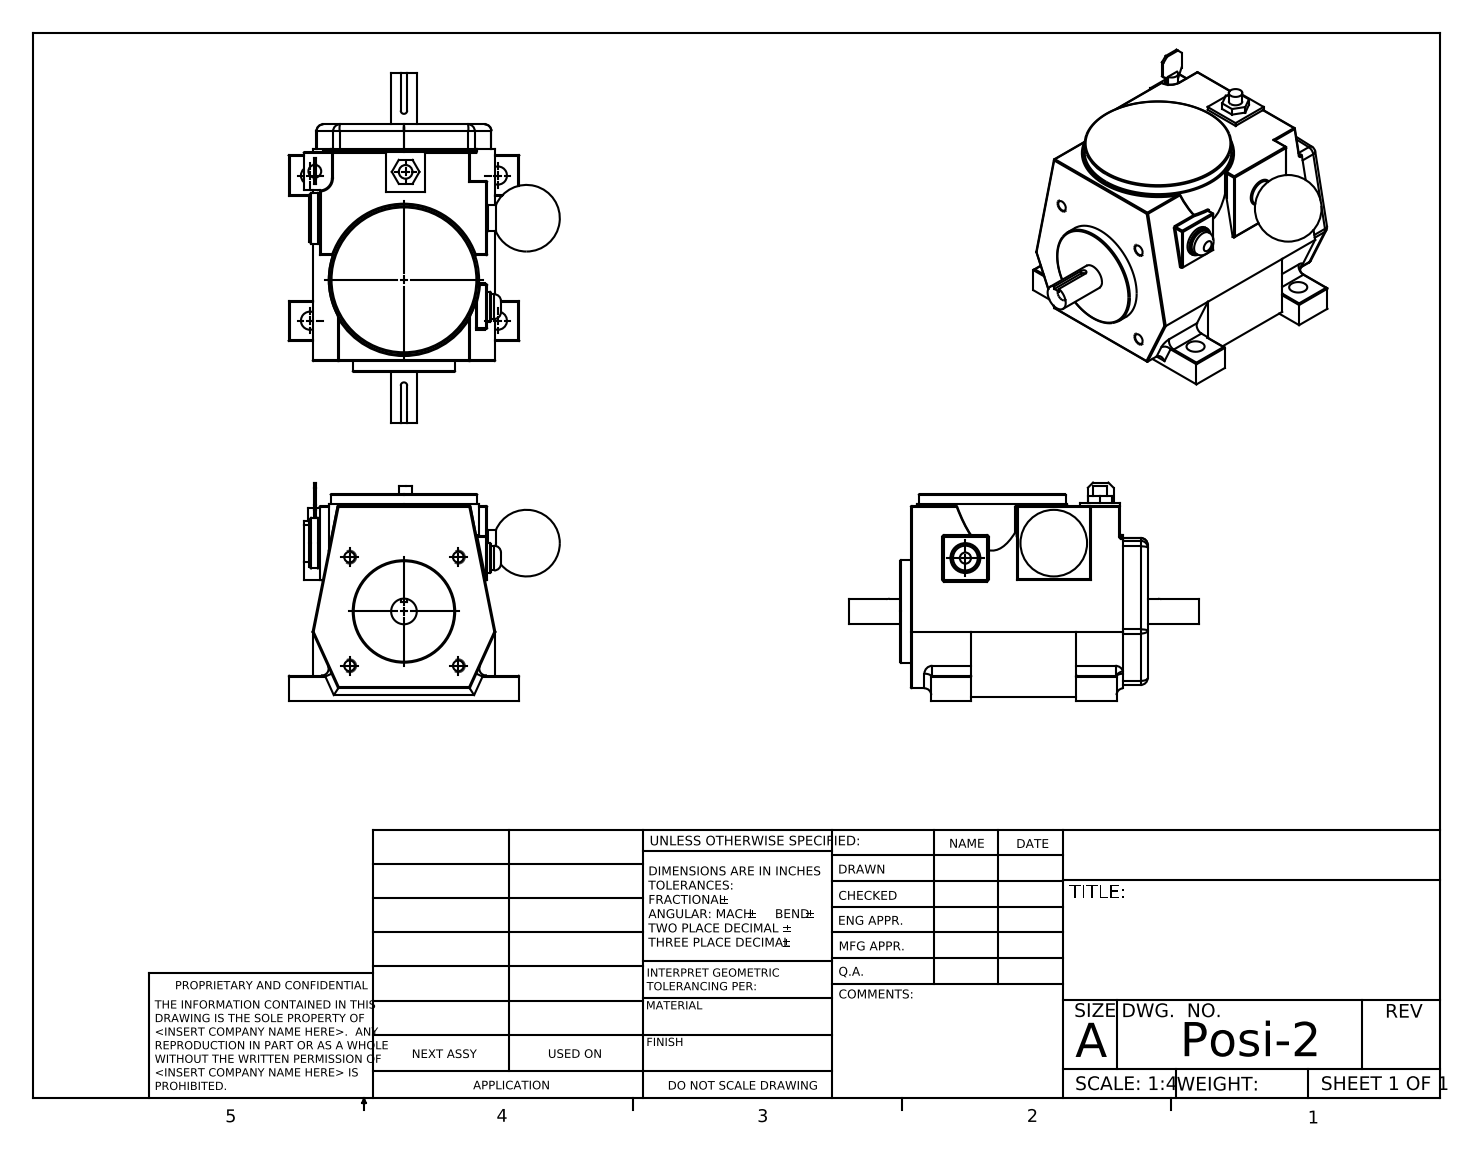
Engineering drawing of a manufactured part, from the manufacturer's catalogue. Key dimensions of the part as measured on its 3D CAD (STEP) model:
Part name (STEP PRODUCT): Posi-2
STEP written by: SolidWorks 2010 (CONFIG_CONTROL_DESIGN)
Units: inches
Bodies: 1 solid, 293 faces (104 planar, 125 cylindrical, 64 other)
Overall size (bounding box): 10.25 × 7.938 × 6.398
Volume: 200.2 in³ · Surface area: 254.4 in²
Round holes (diameter × count): ⌀0.313 ×4, ⌀0.531 ×4
Round bosses / shafts (diameter × count): ⌀0.75 ×2, ⌀4.4 ×1, ⌀4.3 ×1, ⌀3 ×1, ⌀1.48 ×1, ⌀0.875 ×1, ⌀0.725 ×1, ⌀0.4 ×1
Partial cylindrical surfaces — rounded edges, fillets, slot ends (radius × count): R0.03 ×47, R0.2 ×22, R0.094 ×2, R0.36 ×1, R0.977 ×1
Main face-to-face distances: 6.937, 0.125, 6.063, 5.938, 0.35, 5.588, 5.713, 7.25, 0.312, 5.35
Hole centre spacings: 3.182, 3.182, 4.25, 4.5, 5.5, 6.95
